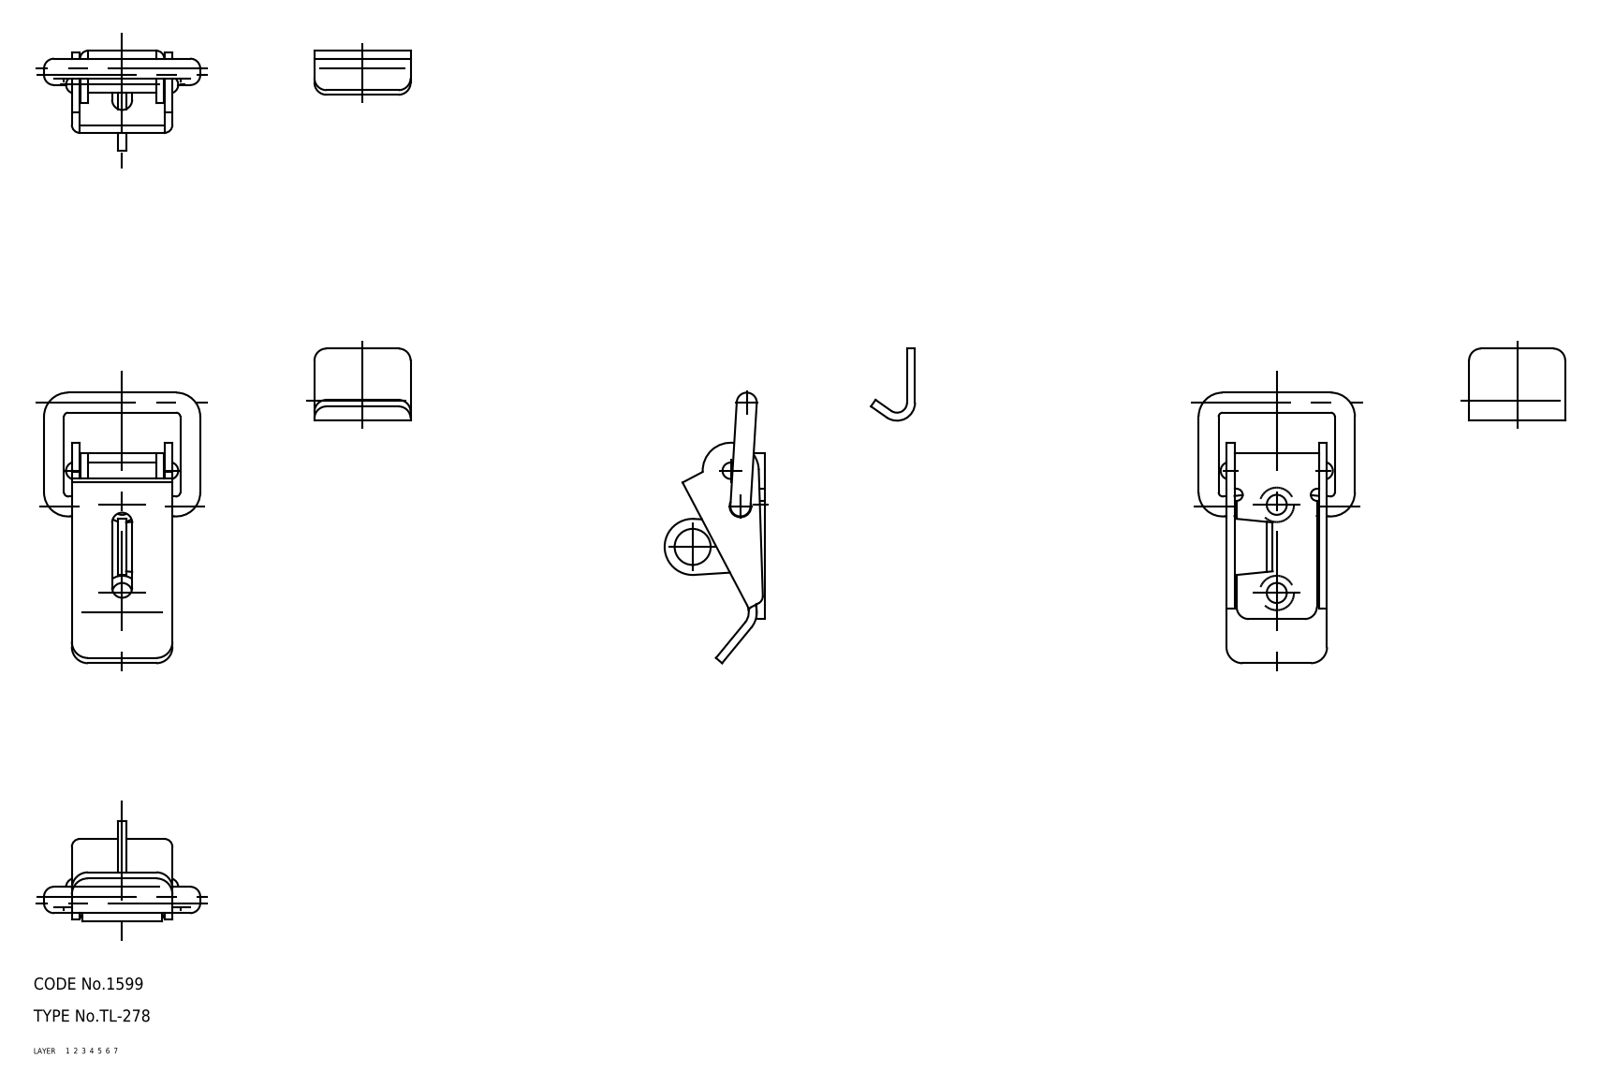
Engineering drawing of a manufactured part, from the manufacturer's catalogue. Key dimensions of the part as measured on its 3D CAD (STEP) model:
Part name (STEP PRODUCT): shaft; lever; keeper; base (+2 more)
STEP written by: CADfix (AUTOMOTIVE_DESIGN)
Units: millimetres
Bodies: 5 solids, 112 faces (0 planar, 0 cylindrical, 112 other)
Overall size (bounding box): 78.53 × 39.03 × 25
Volume: 9 521 mm³ · Surface area: 10 554 mm²
